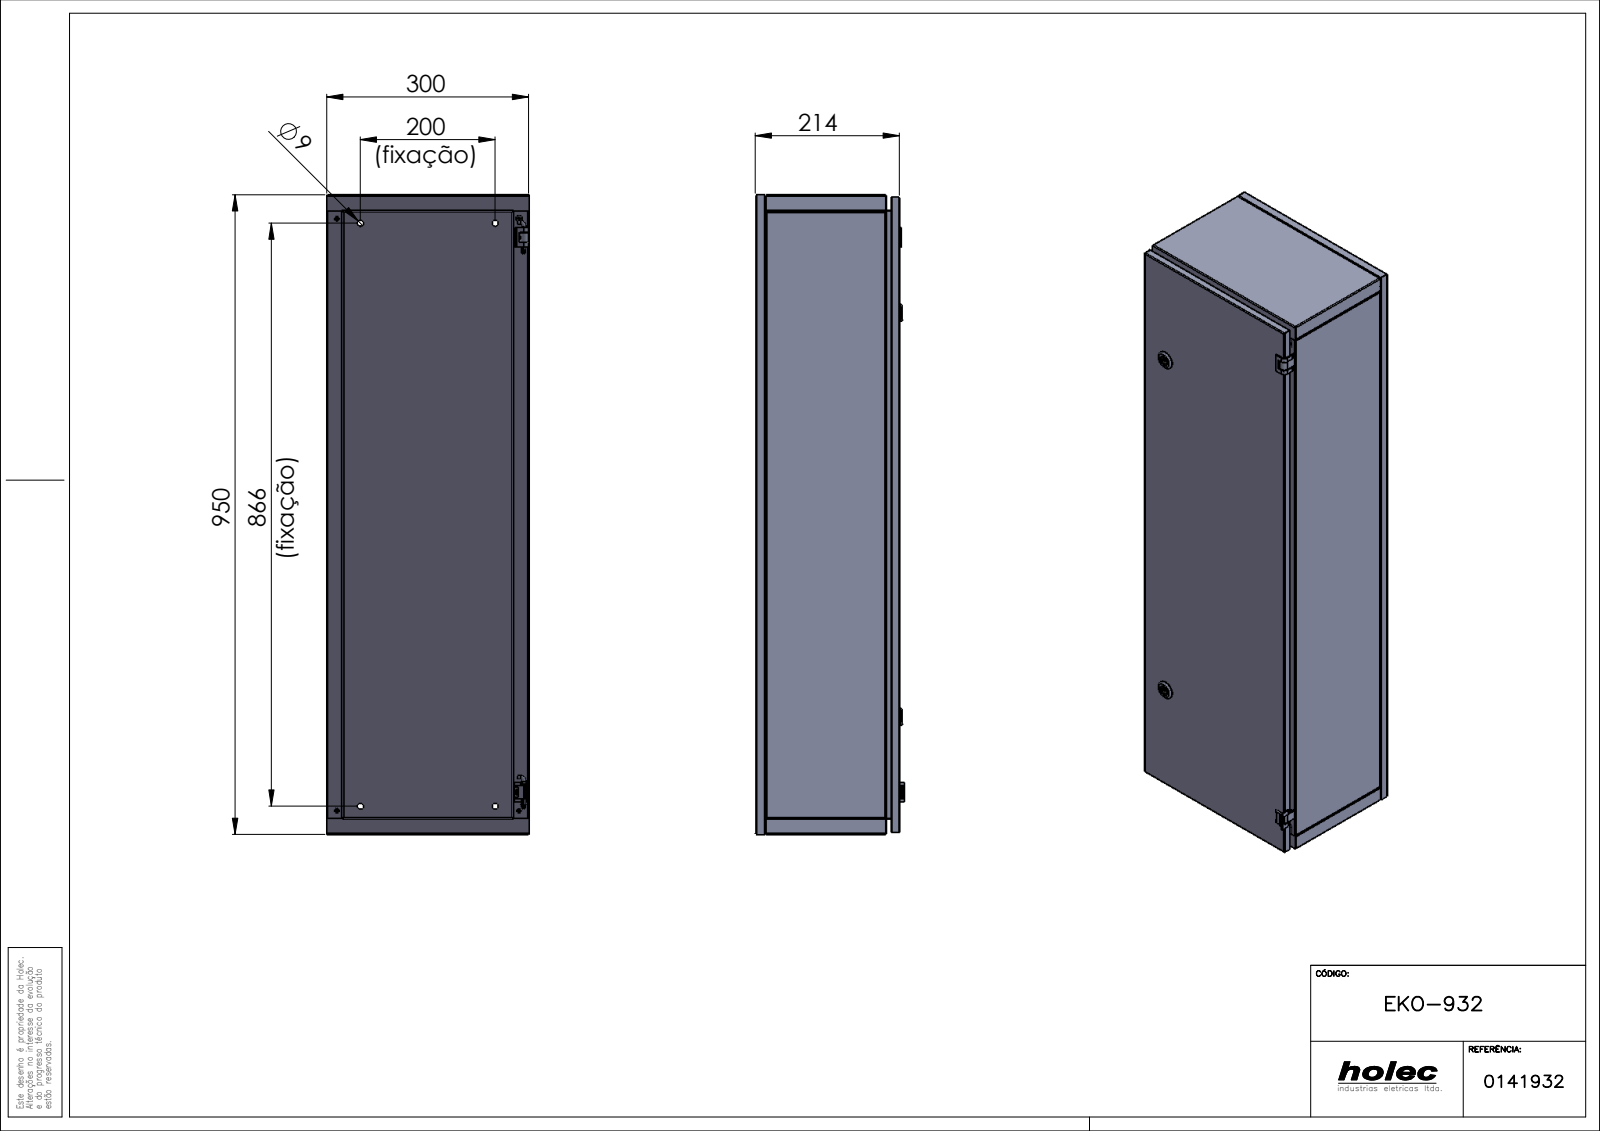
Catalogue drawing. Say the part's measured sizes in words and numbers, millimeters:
The part is named "EKO-932". Its 3-D file was written by "SolidWorks 2017 (AUTOMOTIVE_DESIGN)". It is 53 solids with 2538 faces: 1166 planar, 792 cylindrical and 580 other. Overall it measures 950 by 300 by 220.88 millimeters. Its volume is 1 427 000 cubic millimeters and its surface area 2 814 000 square millimeters. Round holes: 14 of diameter 4.2, 14 of diameter 6, 12 of diameter 4.3, 8 of diameter 7.52, 6 of diameter 1.8, 4 of diameter 5, 4 of diameter 5.5, 4 of diameter 9, 4 of diameter 11, 2 of diameter 3.3, 2 of diameter 4.1, 2 of diameter 6.5. Round bosses or shafts: 8 of diameter 7, 6 of diameter 3.2, 2 of diameter 28, 2 of diameter 19, 2 of diameter 15.7, 2 of diameter 15, 2 of diameter 12.7, 2 of diameter 5.15. Partial cylindrical surfaces (rounded edges, fillets, slot ends): 88 of radius 0.2, 50 of radius 1.5, 48 of radius 0.5, 20 of radius 0.3, 10 of radius 1, 4 of radius 1.05, 4 of radius 2, 4 of radius 2.5. The main face-to-face distances are 1, 213.1, 299, 214.1, 212.1, 300, 298, 24, 949, 22.9. The hole center spacings are 25, 231.35, 50, 230, 235.37, 75, 241.92, 936.33.
